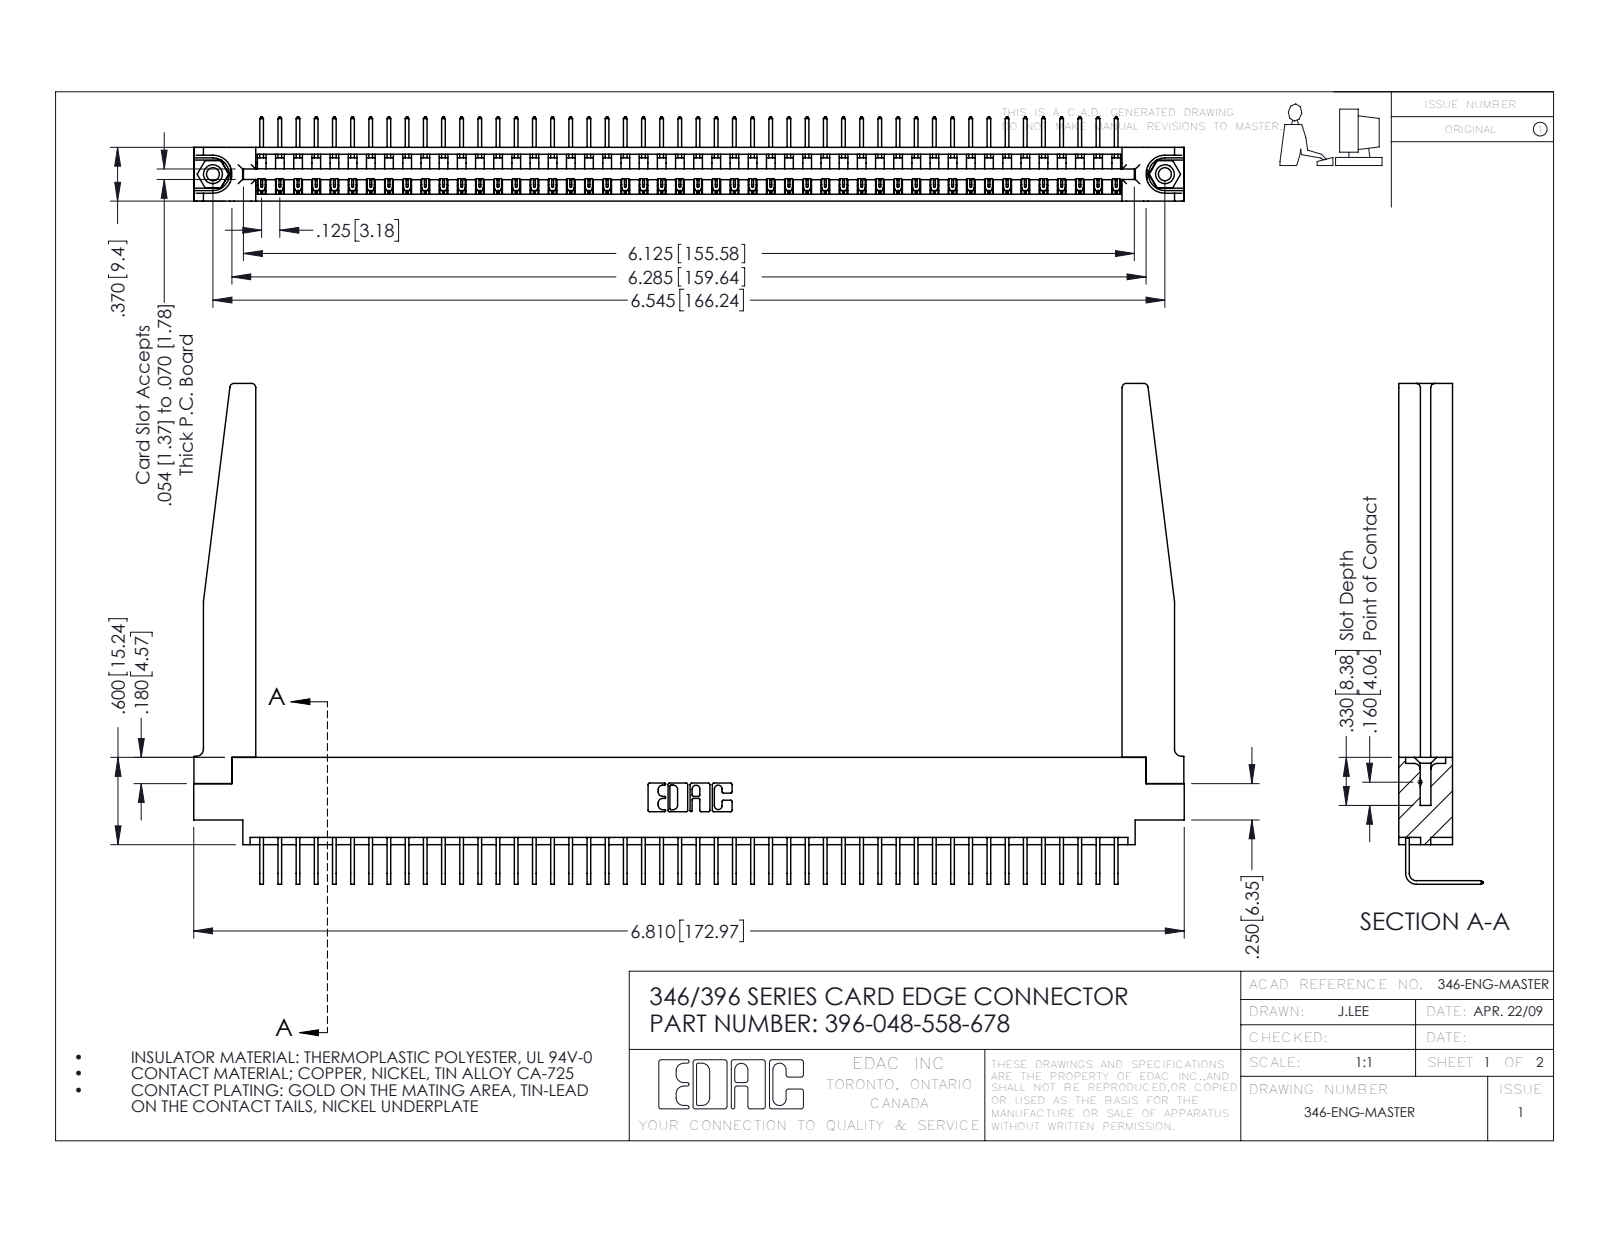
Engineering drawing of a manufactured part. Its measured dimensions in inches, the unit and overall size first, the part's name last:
Units: inches
Overall size (bounding box): 6.81 × 3.443 × 0.58
Round holes (diameter × count): ⌀0.089 ×2, ⌀0.125 ×2, ⌀0.156 ×2, ⌀0.064 ×1
Round bosses / shafts (diameter × count): ⌀0.155 ×2
Partial cylindrical surfaces — rounded edges, fillets, slot ends (radius × count): R0.006 ×96, R0.01 ×22, R0.03 ×8, R0.007 ×6, R0.031 ×6, R0.026 ×3, R0.05 ×3, R0.031 ×2
Main face-to-face distances: 0.37, 0.322, 0.048, 0.072, 0.148, 0.298, 0.025, 0.15, 0.25, 0.222
Hole centre spacings: 0.246, 6.336, 6.545
Volume: 1.435 in³ · Surface area: 44.13 in²
Bodies: 53 solids, 3240 faces (2238 planar, 950 cylindrical, 52 other)
Part name (STEP PRODUCT): 346-220-078_345-220-078; 396-048-558-678; 345-250-001_345-250-001-102; 346 Part_0.170 Offset - 0.156 Dia-TH (+1 more)
STEP written by: SolidWorks 2016 (CONFIG_CONTROL_DESIGN)
